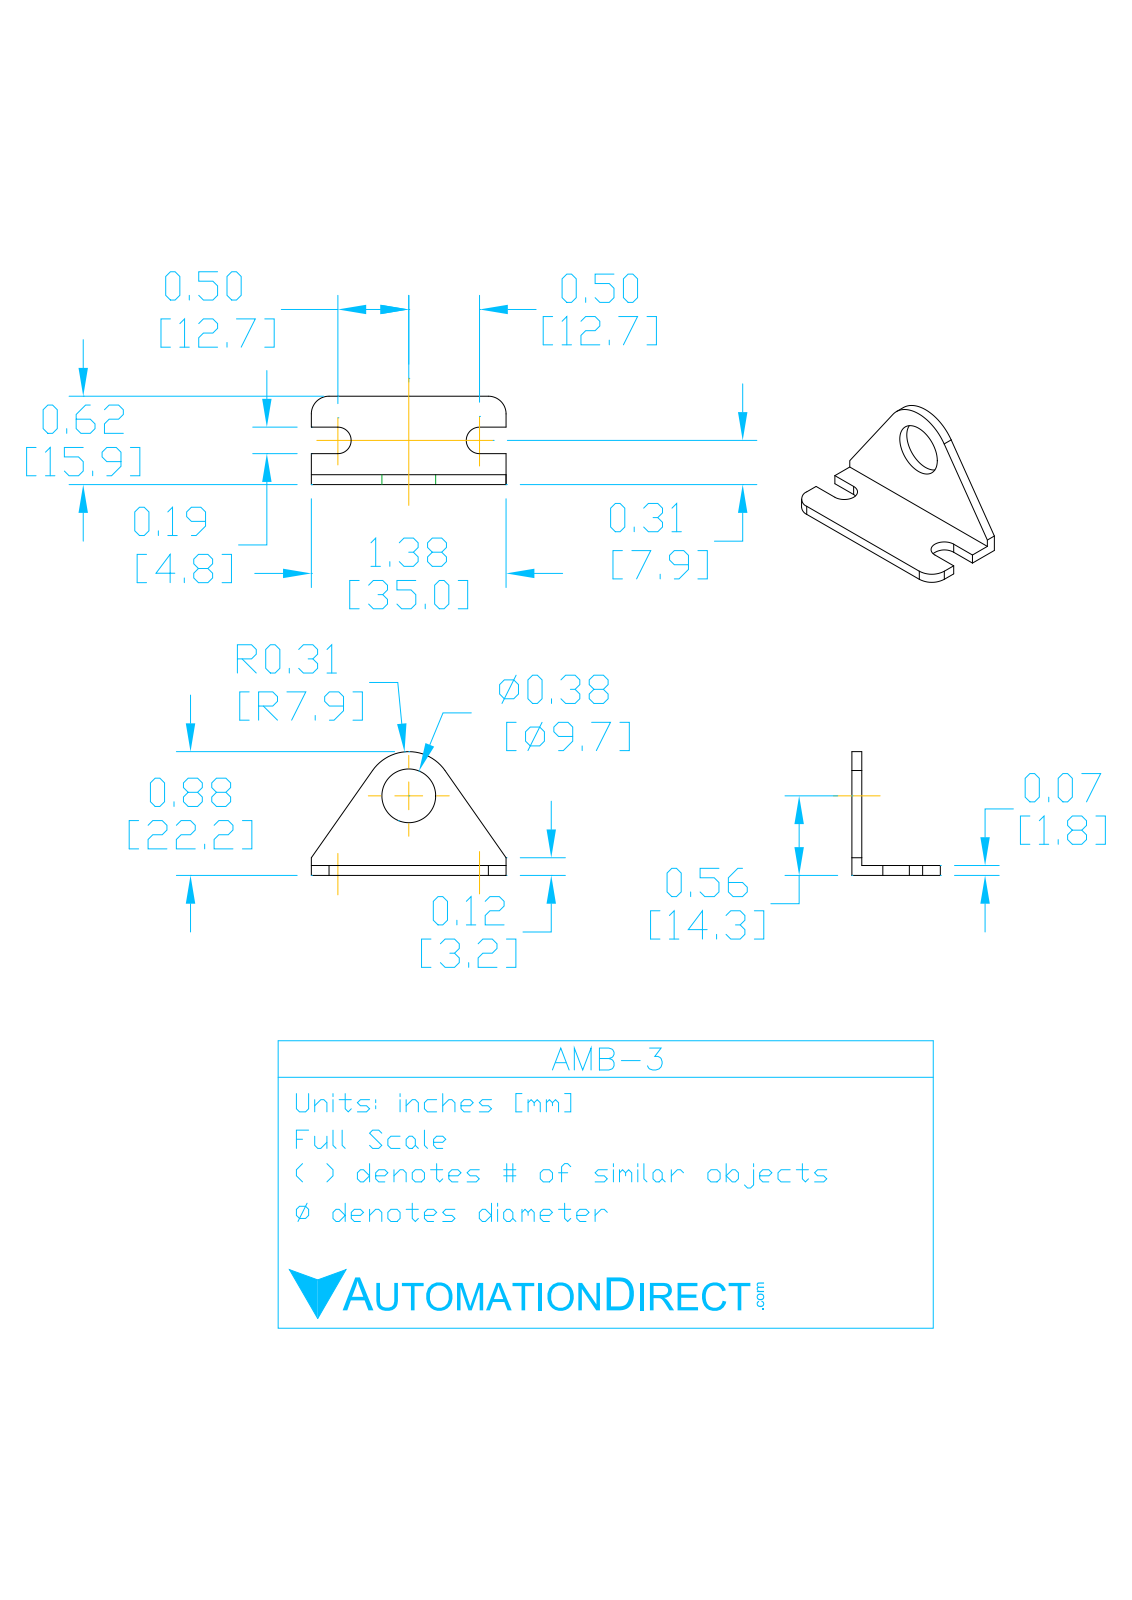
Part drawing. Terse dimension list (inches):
name: AMB-3
written by: SolidWorks 2017 (AUTOMOTIVE_DESIGN)
unit: in
bodies: 1 solid, 28 faces (19 planar, 9 cylindrical, 0 other)
size: 1.375 × 0.87 × 0.625
volume: 0.091 in³; area: 3.052 in²
holes: 1× ⌀0.375
rounds: 2× R0.094, 2× R0.125, 1× R0.06, 1× R0.131, 1× R0.31
face distances: 0.071, 0.554, 0.625, 0.218, 0.407, 0.336, 0.189, 0.147, 1.375, 0.131
